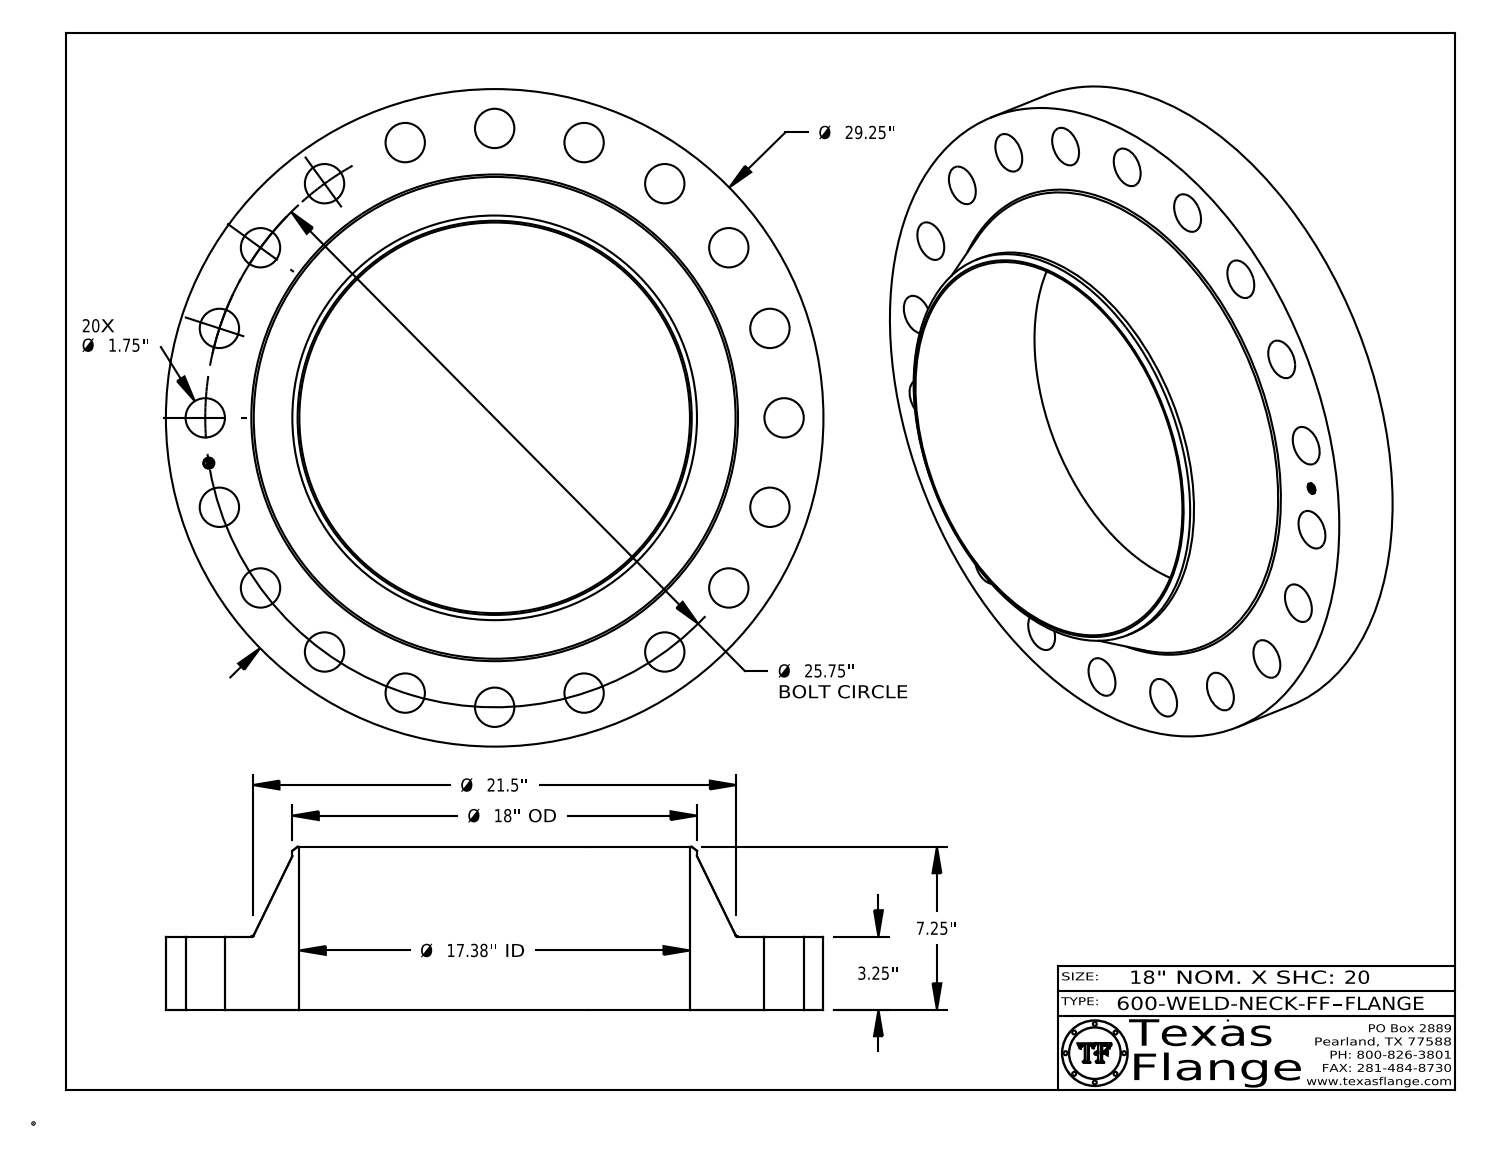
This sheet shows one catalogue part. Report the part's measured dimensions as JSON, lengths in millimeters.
{"part_name": "600-WELD-NECK-FF", "step_written_by": "CATIA V5 STEP AP214 (AUTOMOTIVE_DESIGN)", "units": "millimeters", "bodies": {"solids": 1, "faces": 440, "planar": 368, "cylindrical": 66, "other": 6}, "overall_size": [743, 743, 184.2], "volume_mm3": 24810000, "surface_area_mm2": 1277000, "round_holes": [[44.5, 20], [12.6, 1], [441.4, 1]], "round_bosses_or_shafts": [[0.8, 8], [743, 1], [457.2, 1], [9.9, 1]], "face_to_face_distances": [82.6, 184.2, 101.6, 0.4, 82.2, 102, 3.8, 3.7, 0.7, 2.4], "hole_center_spacings": [327, 622, 646, 202.1, 297, 102.3, 384.4, 462.5]}
